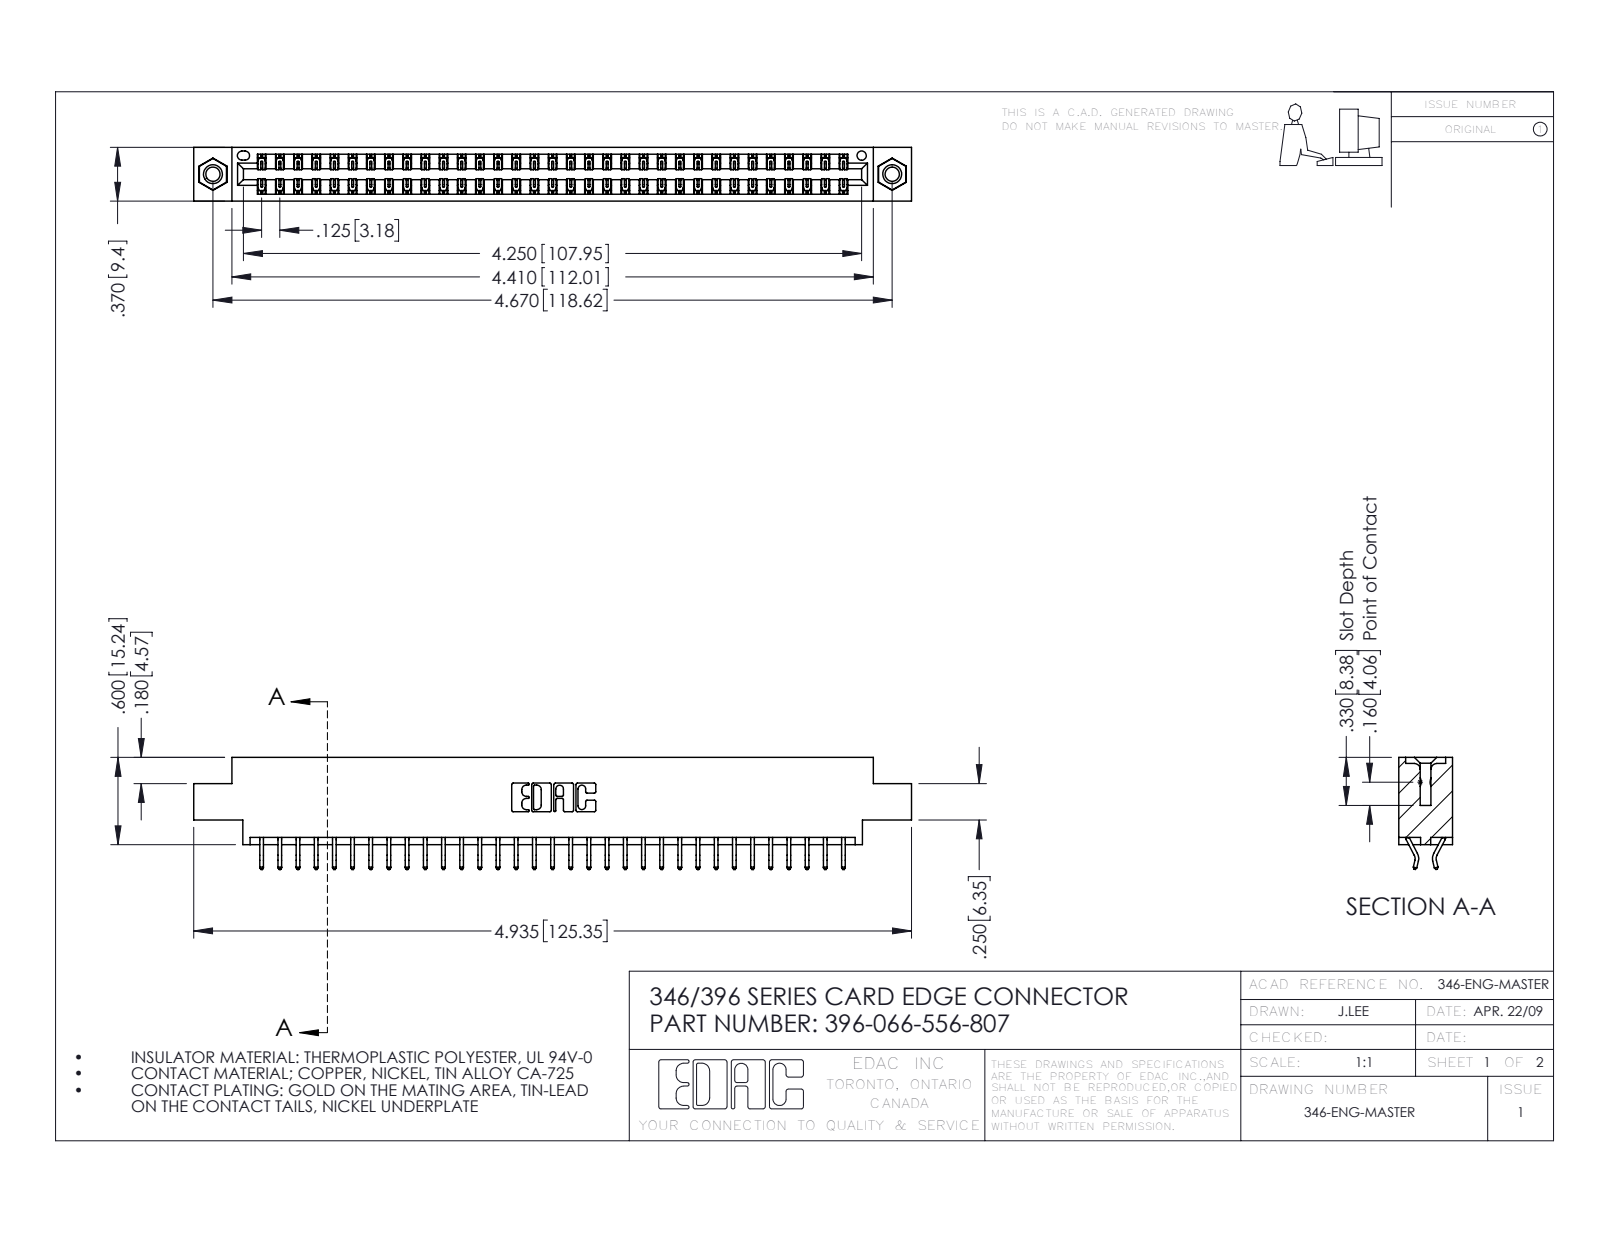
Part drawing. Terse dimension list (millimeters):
name: 345-250-001_345-250-005-103; 396-066-556-807; 345-292-001_556 Tail; 346 Part_0.170 Offset - 0.156 Dia-TI
written by: SolidWorks 2016 (CONFIG_CONTROL_DESIGN)
unit: mm
bodies: 69 solids, 4014 faces (2686 planar, 1312 cylindrical, 16 other)
size: 125.3 × 19.6 × 9.4
volume: 12 000 mm³; area: 16 480 mm²
holes: 2× ⌀2.5, 2× ⌀3.2, 2× ⌀4, 1× ⌀1.6
bosses: 2× ⌀3.9
rounds: 99× R0.2, 22× R0.3, 6× R0.2, 6× R0.8, 3× R0.7, 2× R0.3, 2× R0.4, 2× R0.6
face distances: 1.2, 8.2, 9.4, 6.4, 0.6, 1.8, 7.6, 7, 5.6, 3.8
hole spacings: 6.2, 113.3, 118.6
